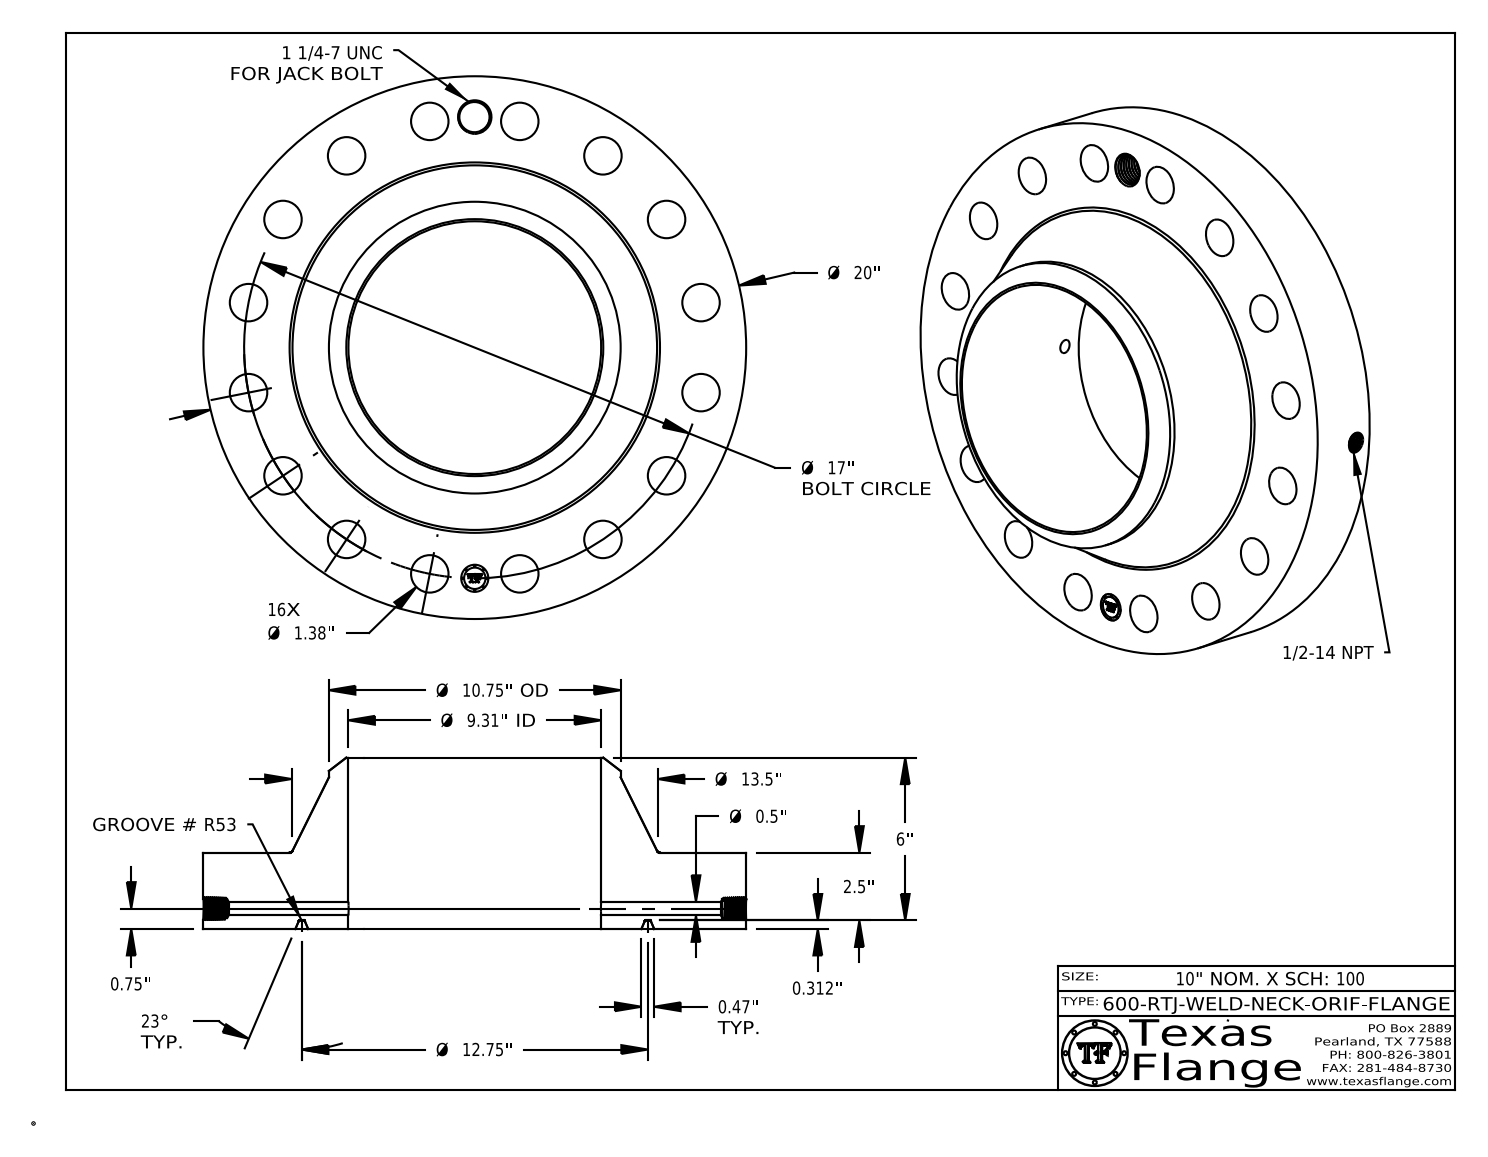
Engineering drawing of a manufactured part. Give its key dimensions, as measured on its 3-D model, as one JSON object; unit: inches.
{"part_name": "600-RTJ-WELD-NECK", "step_written_by": "CATIA V5 STEP AP214 (AUTOMOTIVE_DESIGN)", "units": "inches", "bodies": {"solids": 1, "faces": 822, "planar": 370, "cylindrical": 117, "other": 335}, "overall_size": [20, 20, 6.312], "volume_in3": 758.9, "surface_area_in2": 1128, "round_holes": [[1.38, 16], [0.5, 1], [0.672, 1], [1, 1], [1.109, 1], [9.312, 1]], "round_bosses_or_shafts": [[0.061, 8], [20, 1], [10.75, 1], [0.788, 1]], "face_to_face_distances": [2.812, 0.312, 2.5, 6.312, 6, 3.5, 2.797, 2.485, 0.015, 3.515], "hole_center_spacings": [8.5, 12.021, 15.706, 16.673, 3.317, 9.444, 14.135, 17]}
